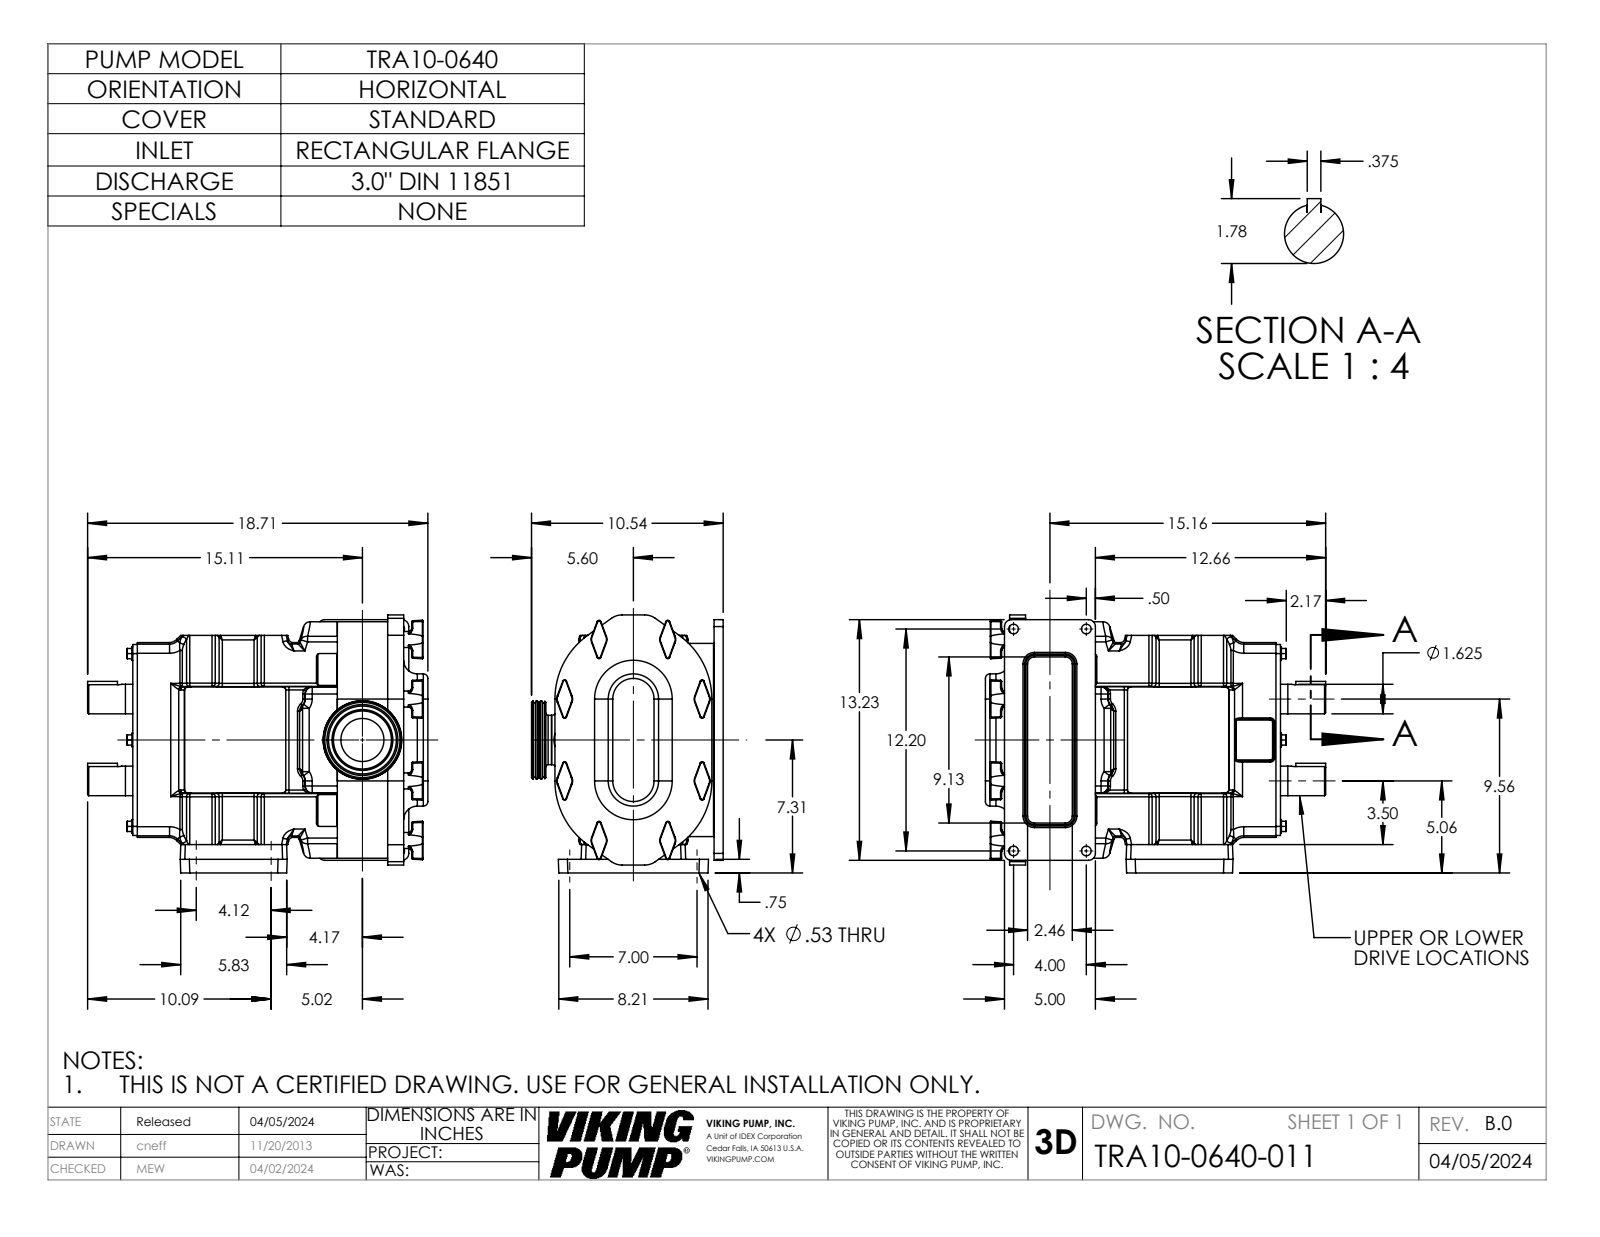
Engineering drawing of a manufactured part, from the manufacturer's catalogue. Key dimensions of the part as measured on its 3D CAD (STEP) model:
Part name (STEP PRODUCT): TRA10-0640-BODY; 0600DIN11851-30; TRA10-0640-011; TRA10-0600-GEARBOX-H (+1 more)
STEP written by: SolidWorks 2022 (AUTOMOTIVE_DESIGN)
Units: inches
Bodies: 4 solids, 1106 faces (297 planar, 393 cylindrical, 416 other)
Overall size (bounding box): 18.714 × 14.185 × 10.539
Volume: 1 231 in³ · Surface area: 1 453 in²
Round holes (diameter × count): ⌀0.531 ×8, ⌀2.368 ×1, ⌀3.732 ×1
Round bosses / shafts (diameter × count): ⌀0.88 ×8, ⌀0.75 ×6, ⌀1.624 ×2, ⌀3.346 ×1, ⌀2.708 ×1
Partial cylindrical surfaces — rounded edges, fillets, slot ends (radius × count): R0.18 ×44, R0.06 ×43, R0.03 ×36, R0.38 ×36, R0.25 ×32, R0.12 ×24, R0.5 ×22, R0.09 ×16
Main face-to-face distances: 2.769, 0.5, 7.937, 0.88, 3.649, 1.437, 0.36, 11.25, 14.899, 14.019
Hole centre spacings: 4, 4.12, 6.404, 6.435, 7, 8.122, 12.2, 12.839
